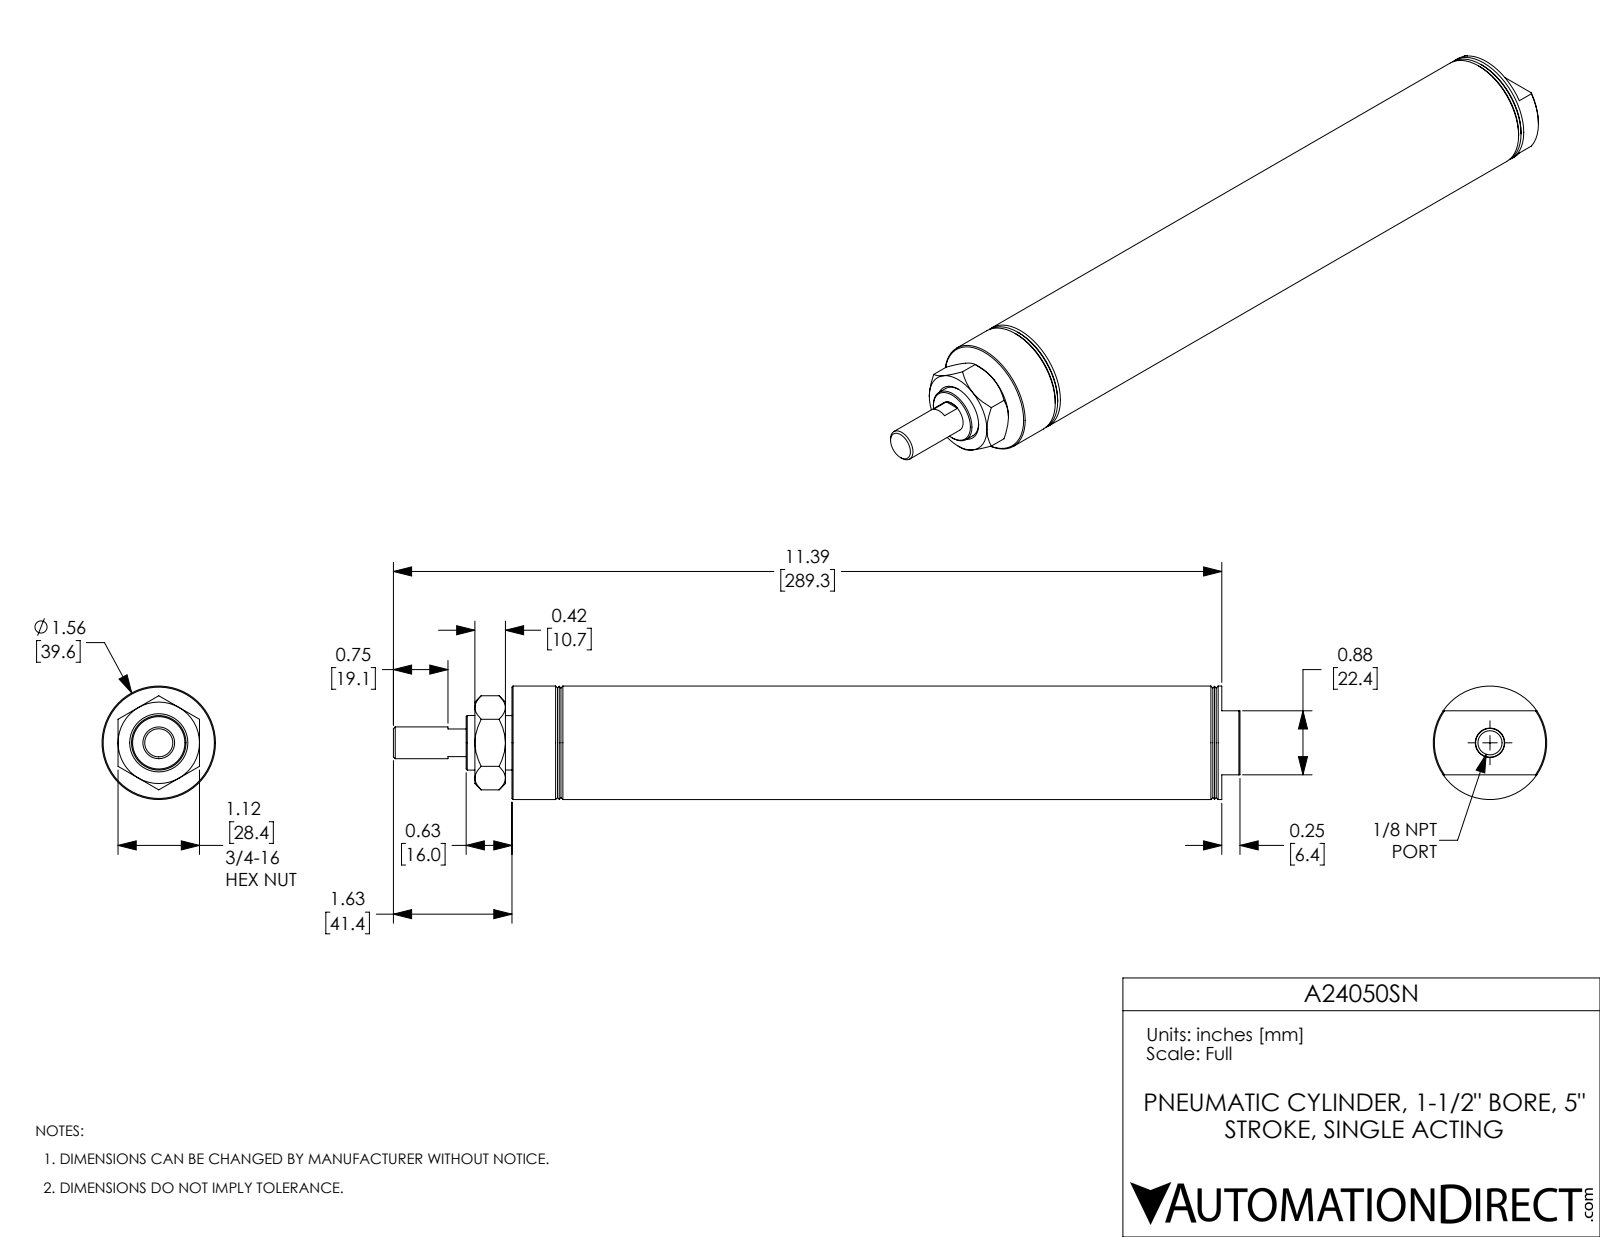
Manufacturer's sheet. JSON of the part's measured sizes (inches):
{"part_name": "A24050SN; A24050SN_Mounting Nut_D-3556; A24050SN-Rod; A24050SN-MainBody", "step_written_by": "SolidWorks 2017 (AUTOMOTIVE_DESIGN)", "units": "inches", "bodies": {"solids": 3, "faces": 93, "planar": 28, "cylindrical": 22, "other": 43}, "overall_size": [11.64, 1.56, 1.56], "volume_in3": 11.37, "surface_area_in2": 111.7, "round_holes": [[0.332, 1], [0.437, 1], [0.75, 1], [1.5, 1]], "round_bosses_or_shafts": [[1.56, 1], [0.747, 1]], "face_to_face_distances": [2.255, 7.755, 0.5, 5.5, 5, 7.255, 2.755, 10.01, 0.25, 1.12]}
